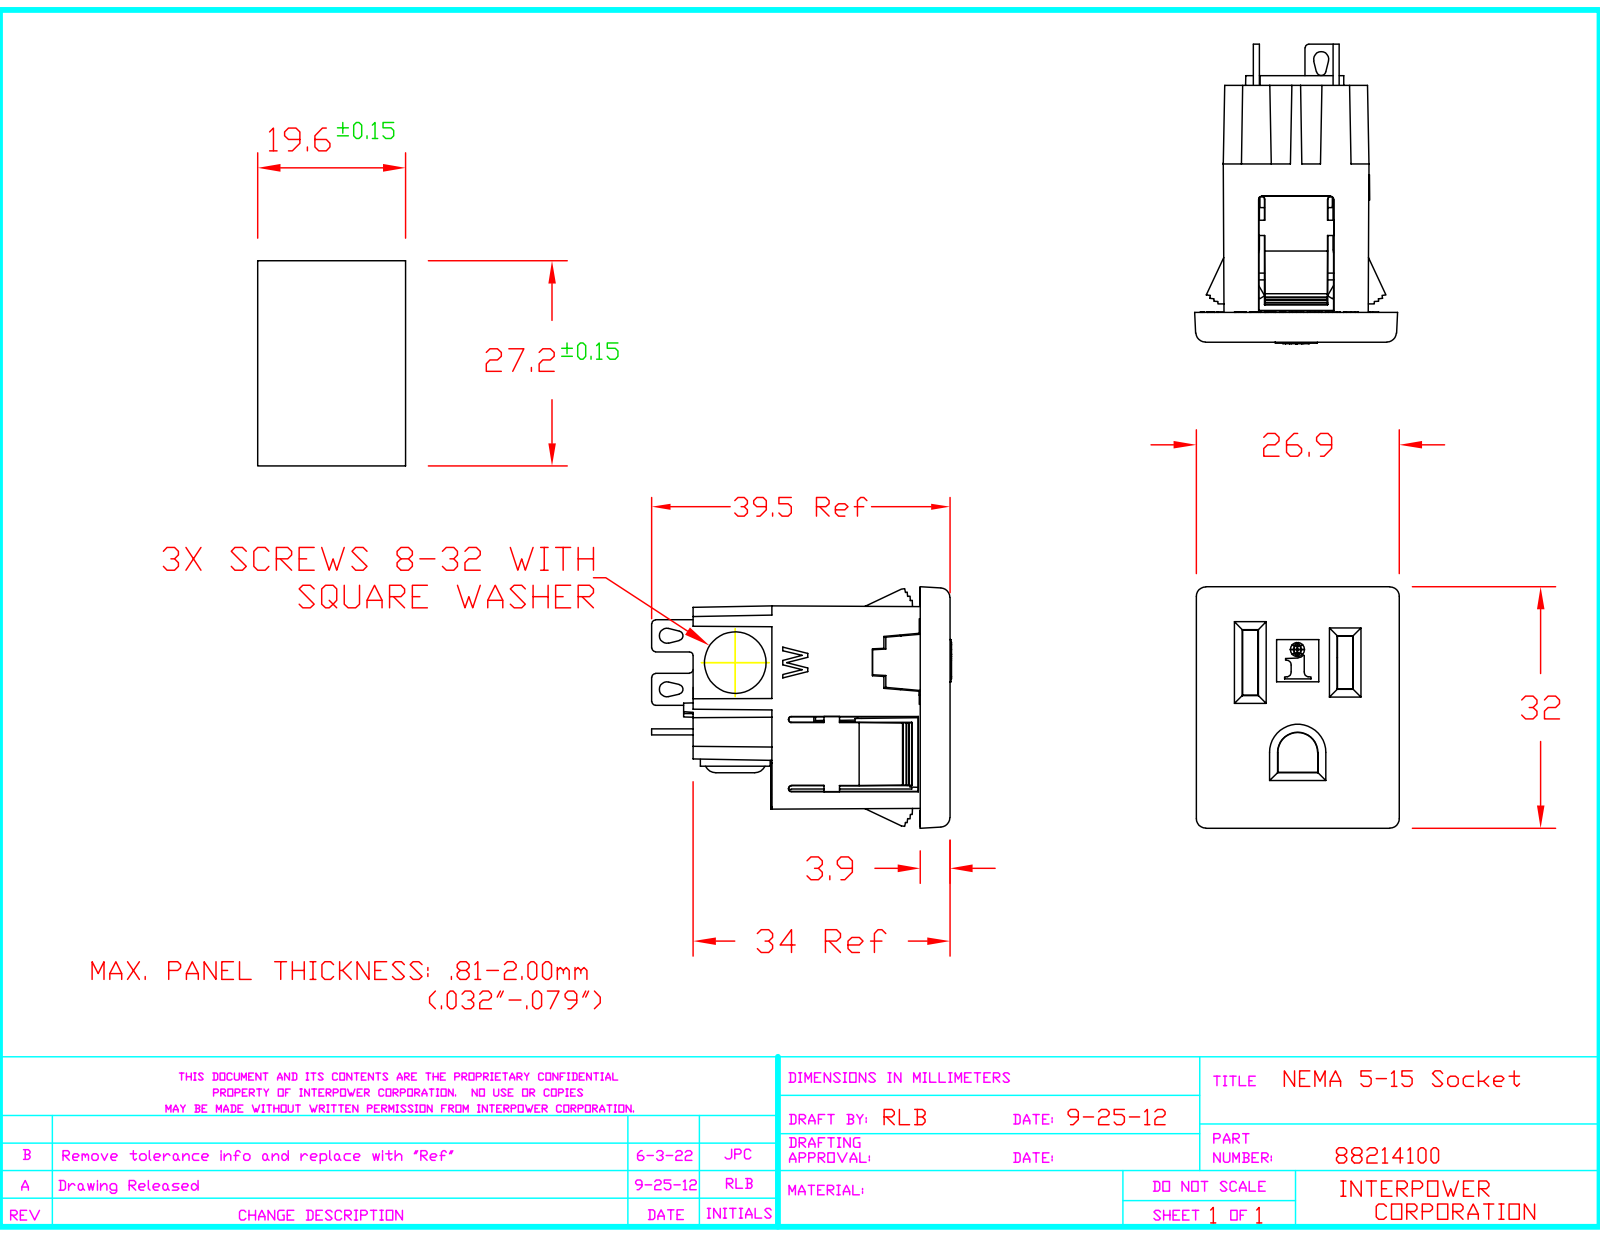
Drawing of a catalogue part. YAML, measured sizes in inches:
part_name: "55030610-R2_NEMA_Contact_Solder-Tab.2; 55030610-R2_NEMA_Contact_Solder-Tab_Assy; 55030780-R4_NEMA-GROUND-SO_11-9-11; Contacts_Solder-Tab_Assy (+8 more)"
step_written_by: "OneSpace Designer 14.50 18-Oct-2006 (C) CoCreate Software GmbH (AUTOMOTIVE_DESIGN)"
units: inches
bodies: {solids: 11, faces: 2599, planar: 2312, cylindrical: 251, other: 36}
overall_size: [1.567, 1.259, 1.059]
volume: 0.61
surface_area: 22.3
round_holes:
  - {diameter: 0.146, count: 2}
  - {diameter: 0.173, count: 2}
round_bosses_or_shafts:
  - {diameter: 0.322, count: 2}
  - {diameter: 0.19, count: 2}
  - {diameter: 0.164, count: 2}
partial_cylinders:
  - {radius: 0.02, count: 45}
  - {radius: 0.015, count: 14}
  - {radius: 0.02, count: 11}
  - {radius: 0.03, count: 8}
  - {radius: 0.035, count: 8}
  - {radius: 0.05, count: 8}
  - {radius: 0.015, count: 7}
  - {radius: 0.052, count: 7}
face_to_face_distances: [0.031, 0.08, 0.69, 0.416, 0.85, 0.775, 0.155, 0.99, 0.99, 0.93]
